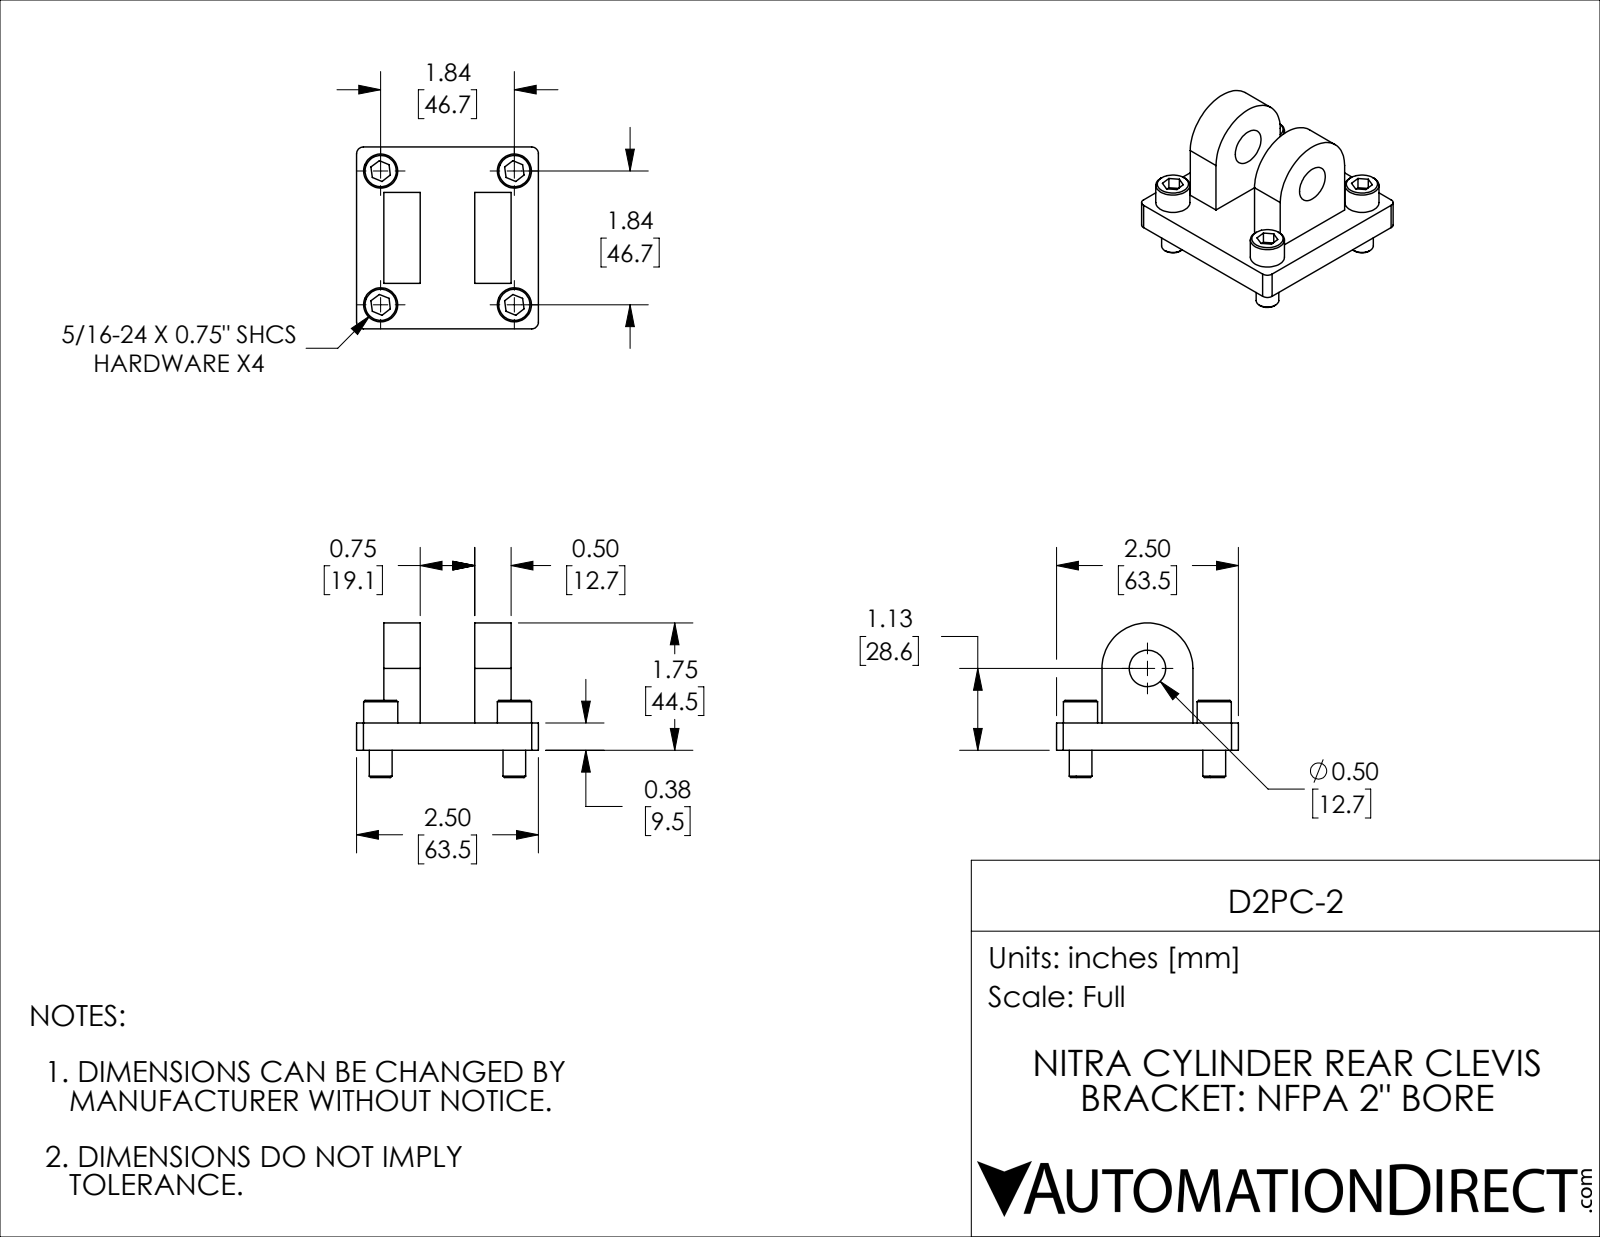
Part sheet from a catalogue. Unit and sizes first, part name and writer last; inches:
Units: inches
Overall size (bounding box): 2.5 × 2.5 × 2.125
Round holes (diameter × count): ⌀0.344 ×4, ⌀0.501 ×1
Round bosses / shafts (diameter × count): ⌀0.469 ×4, ⌀0.312 ×4
Partial cylindrical surfaces — rounded edges, fillets, slot ends (radius × count): R0.093 ×4, R0.625 ×1
Main face-to-face distances: 0.375, 0.5, 1.25, 2.5, 0.625, 1.875, 0.75, 1.75, 0.875, 1.625
Hole centre spacings: 1.838, 2.599
Volume: 3.965 in³ · Surface area: 32.84 in²
Bodies: 5 solids, 104 faces (54 planar, 34 cylindrical, 16 other)
Part name (STEP PRODUCT): D2PC-2
STEP written by: SolidWorks 2019 (CONFIG_CONTROL_DESIGN)
